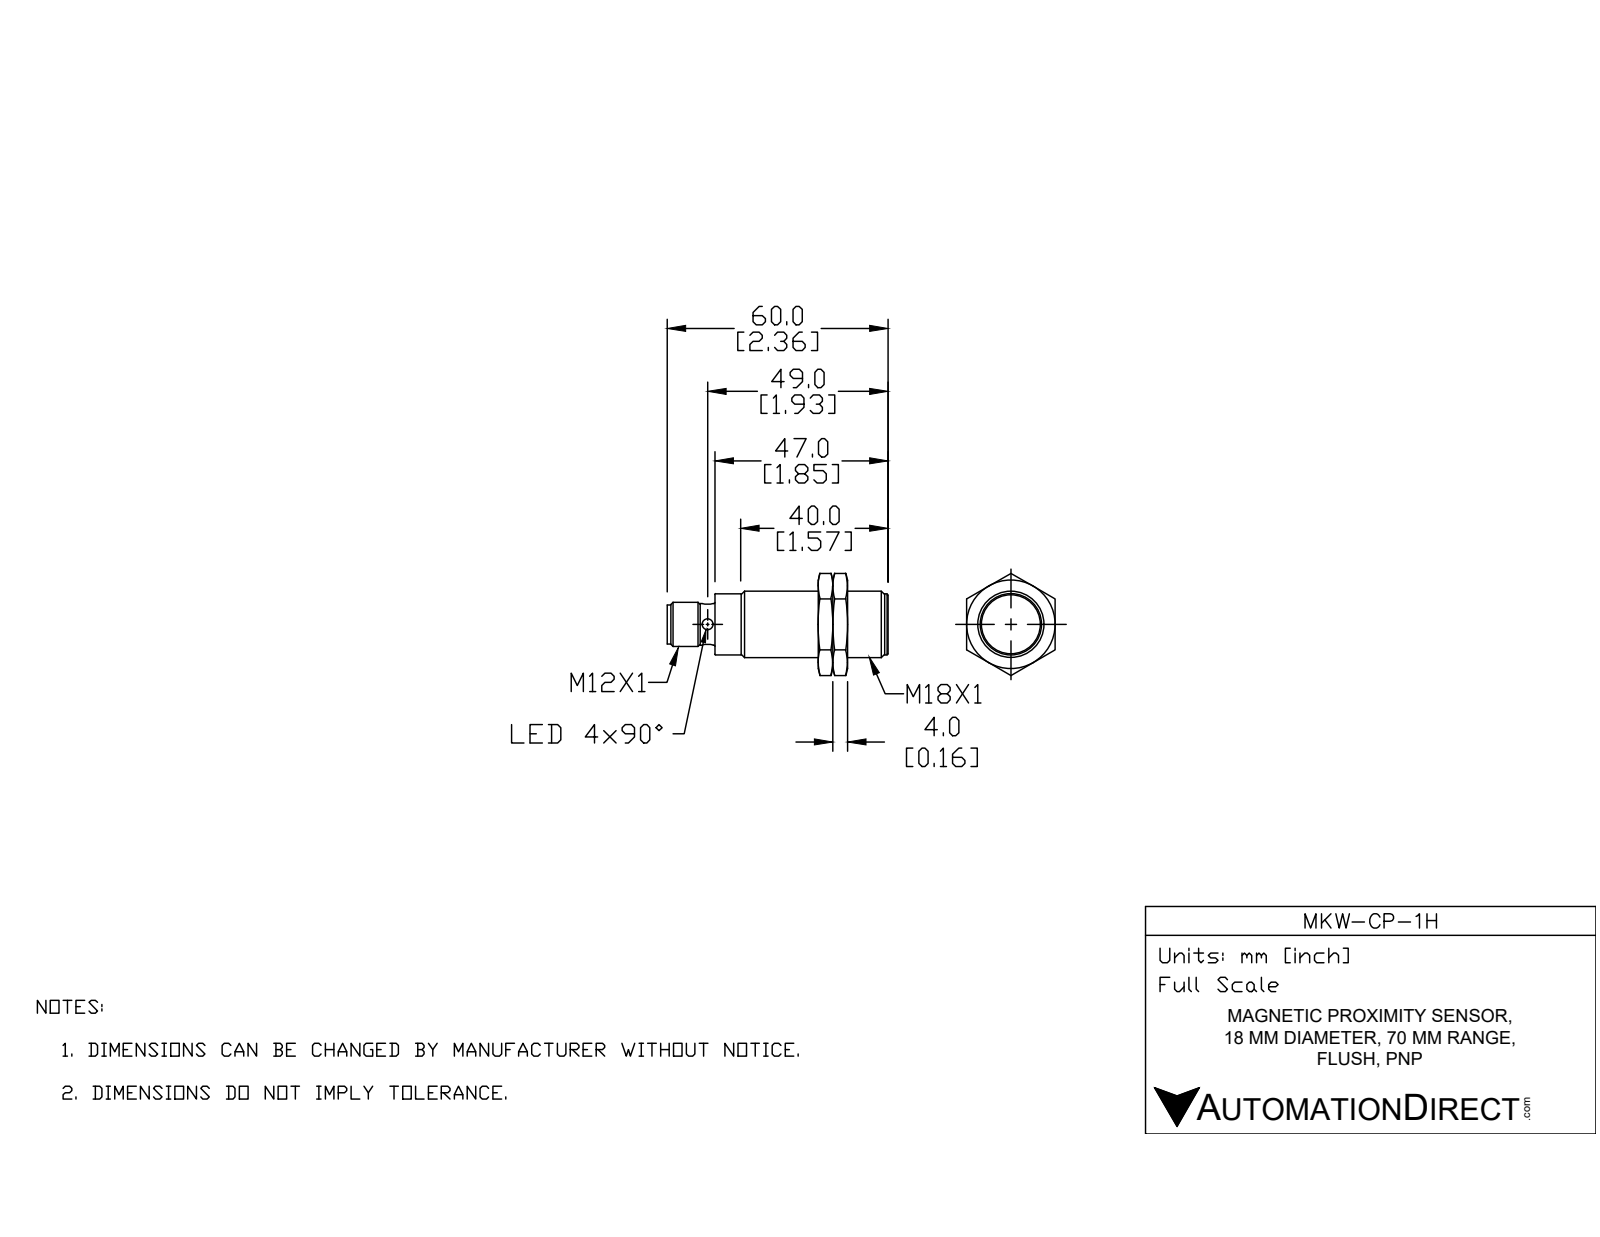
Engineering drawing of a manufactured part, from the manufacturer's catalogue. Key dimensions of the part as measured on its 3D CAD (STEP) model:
STEP written by: unknown (CONFIG_CONTROL_DESIGN)
Units: millimetres
Bodies: 3 solids, 109 faces (26 planar, 33 cylindrical, 50 other)
Overall size (bounding box): 60 × 19.63 × 17
Volume: 7 141 mm³ · Surface area: 3 998 mm²
Round holes (diameter × count): ⌀2.5 ×2, ⌀8.4 ×1, ⌀10.92 ×1
Round bosses / shafts (diameter × count): ⌀12 ×1, ⌀10.6 ×1, ⌀10.5 ×1, ⌀10.3 ×1
Partial cylindrical surfaces — rounded edges, fillets, slot ends (radius × count): R0.6 ×1, R4.5 ×1
Main face-to-face distances: 4, 17, 8, 20, 16, 24, 27.1, 31.1, 35.1, 51.1
